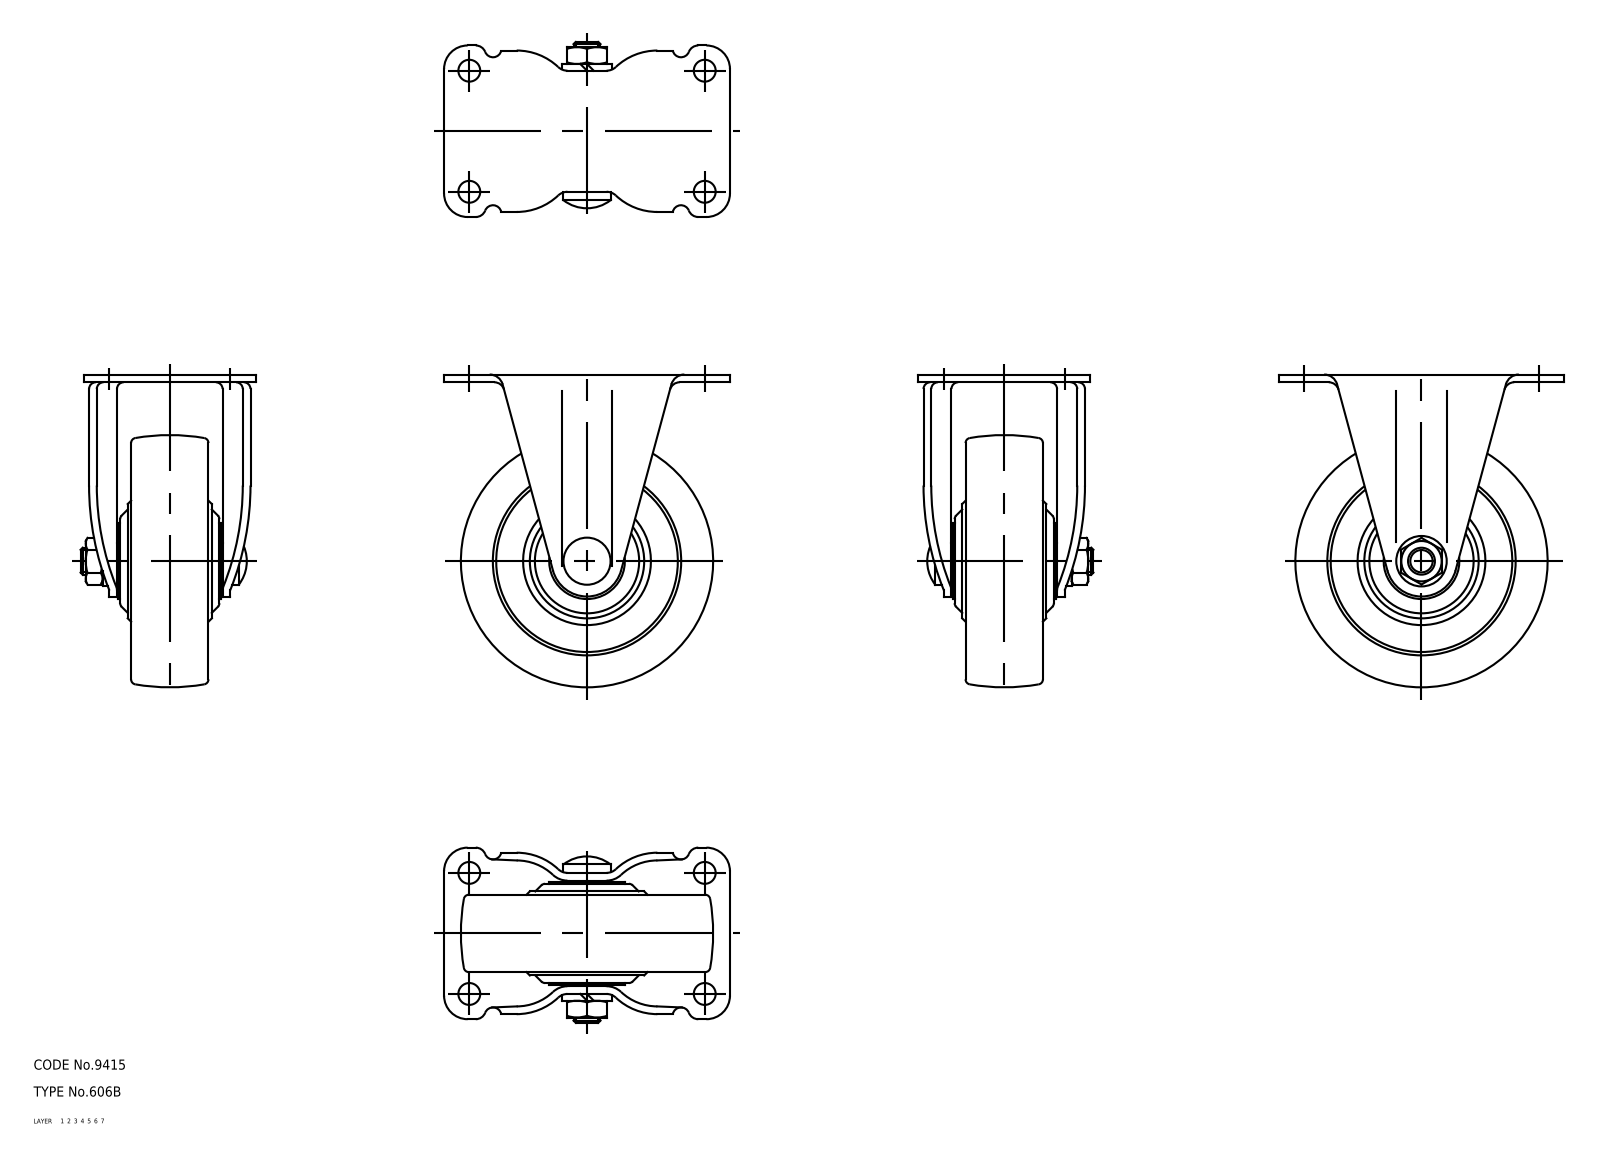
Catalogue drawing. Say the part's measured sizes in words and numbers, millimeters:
The part is named "67121080; 67121093; 67121106". Its 3-D file was written by "CADfix (AUTOMOTIVE_DESIGN)". It is 3 solids with 192 faces: 0 planar, 0 cylindrical and 192 other. Overall it measures 93 by 85 by 52 millimeters. Its volume is 111 914 cubic millimeters and its surface area 36 070 square millimeters.
